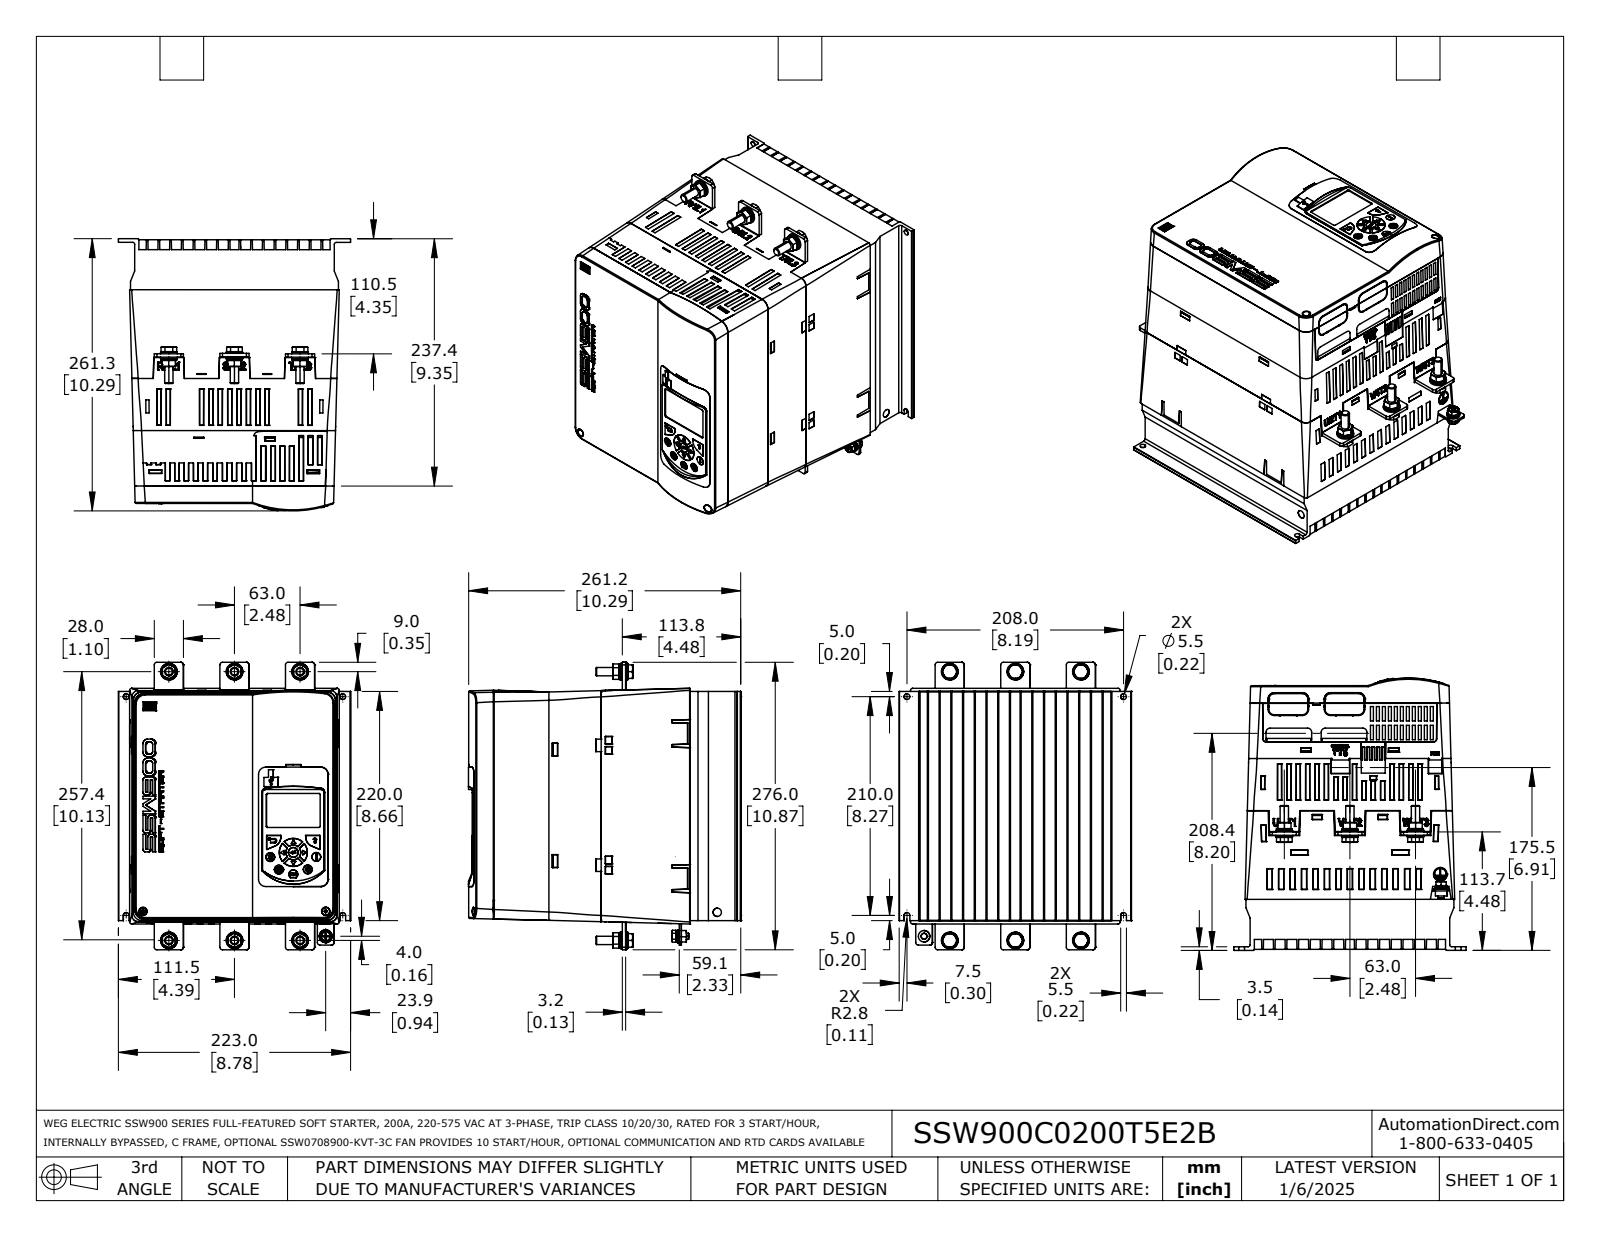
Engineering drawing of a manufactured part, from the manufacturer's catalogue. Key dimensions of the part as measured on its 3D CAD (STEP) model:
Part name (STEP PRODUCT): SSW900C0200T5E2B
STEP written by: SolidWorks 2021 (AUTOMOTIVE_DESIGN)
Units: inches
Bodies: 11 solids, 4292 faces (2981 planar, 513 cylindrical, 798 other)
Overall size (bounding box): 10.866 × 10.296 × 8.78
Volume: 104.6 in³ · Surface area: 1 019 in²
Round holes (diameter × count): ⌀0.315 ×6, ⌀0.094 ×2, ⌀0.217 ×2, ⌀0.096 ×1, ⌀0.133 ×1, ⌀0.197 ×1, ⌀0.294 ×1, ⌀0.335 ×1, ⌀0.406 ×1, ⌀0.453 ×1
Round bosses / shafts (diameter × count): ⌀0.63 ×6, ⌀0.6 ×6, ⌀0.591 ×4, ⌀0.315 ×2, ⌀0.512 ×1, ⌀0.488 ×1, ⌀0.433 ×1, ⌀0.362 ×1
Partial cylindrical surfaces — rounded edges, fillets, slot ends (radius × count): R0.012 ×121, R0.02 ×42, R0.008 ×16, R0.03 ×16, R0.098 ×14, R0.006 ×7, R0.024 ×6, R0.039 ×6
Main face-to-face distances: 7.302, 0.175, 0.102, 9.965, 9.79, 9.863, 9.688, 9.926, 9.751, 0.063
Hole centre spacings: 0.941, 2.48, 8.139, 11.079, 0.981, 1.465, 1.466, 1.471
